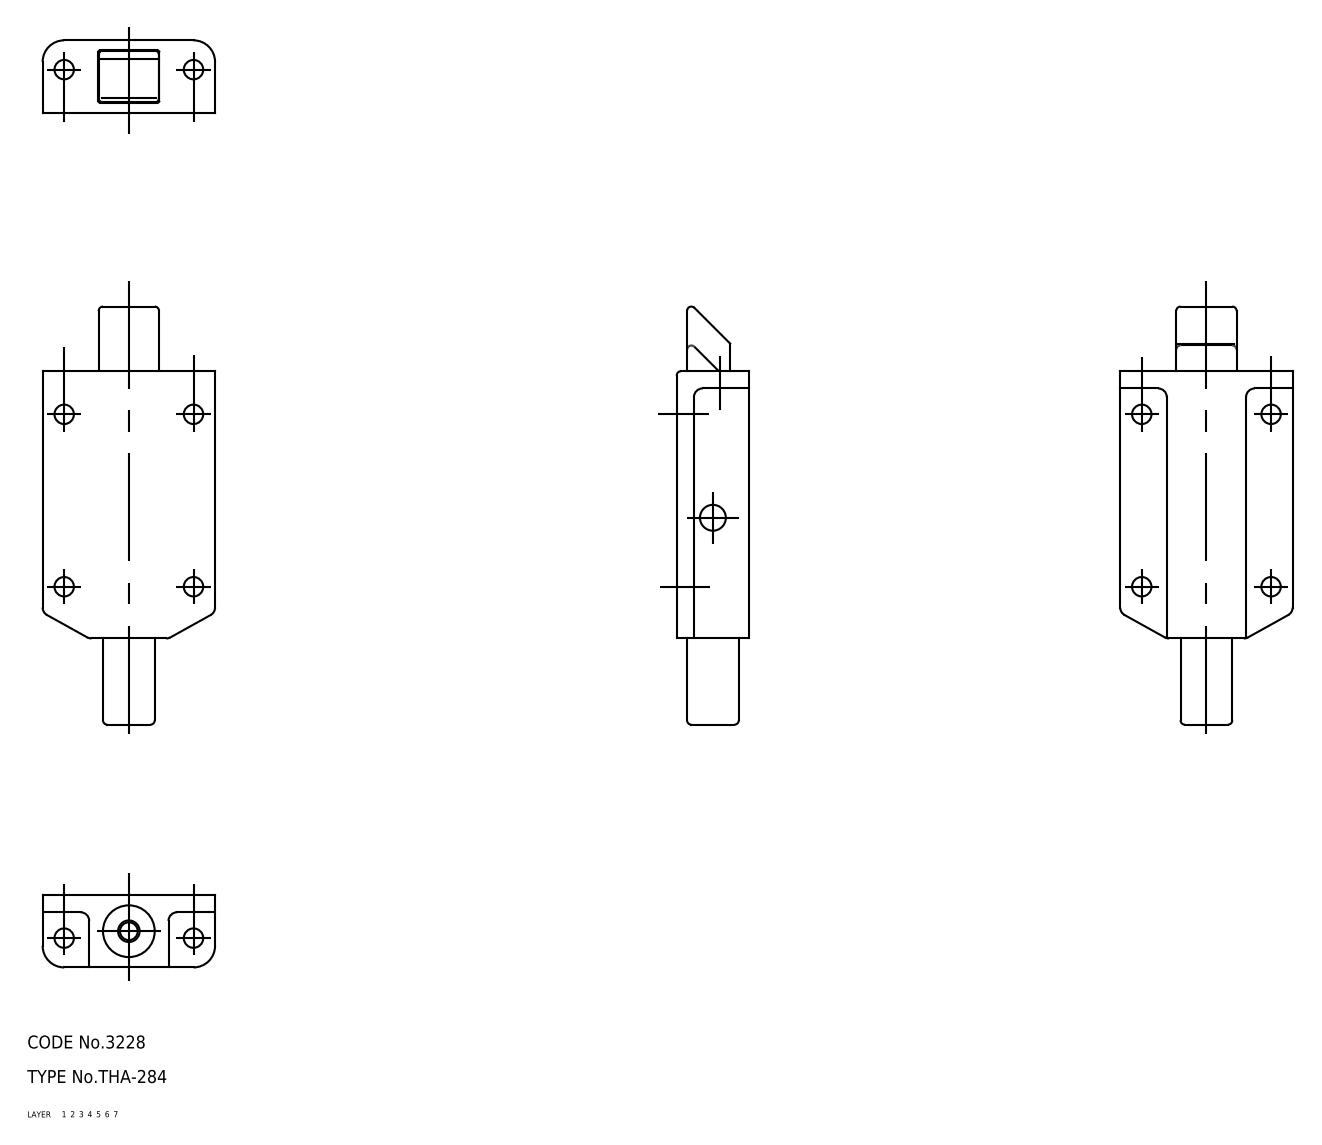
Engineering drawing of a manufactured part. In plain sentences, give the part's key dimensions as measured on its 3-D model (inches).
The part is named "pin; latch; joint; housing (+1 more)". Its 3-D file was written by "CADfix (AUTOMOTIVE_DESIGN)". It is 4 solids with 109 faces: 0 planar, 0 cylindrical and 109 other. Overall it measures 3.819 by 1.575 by 0.661 inches. Its volume is 1.635 cubic inches and its surface area 26.27 square inches.
